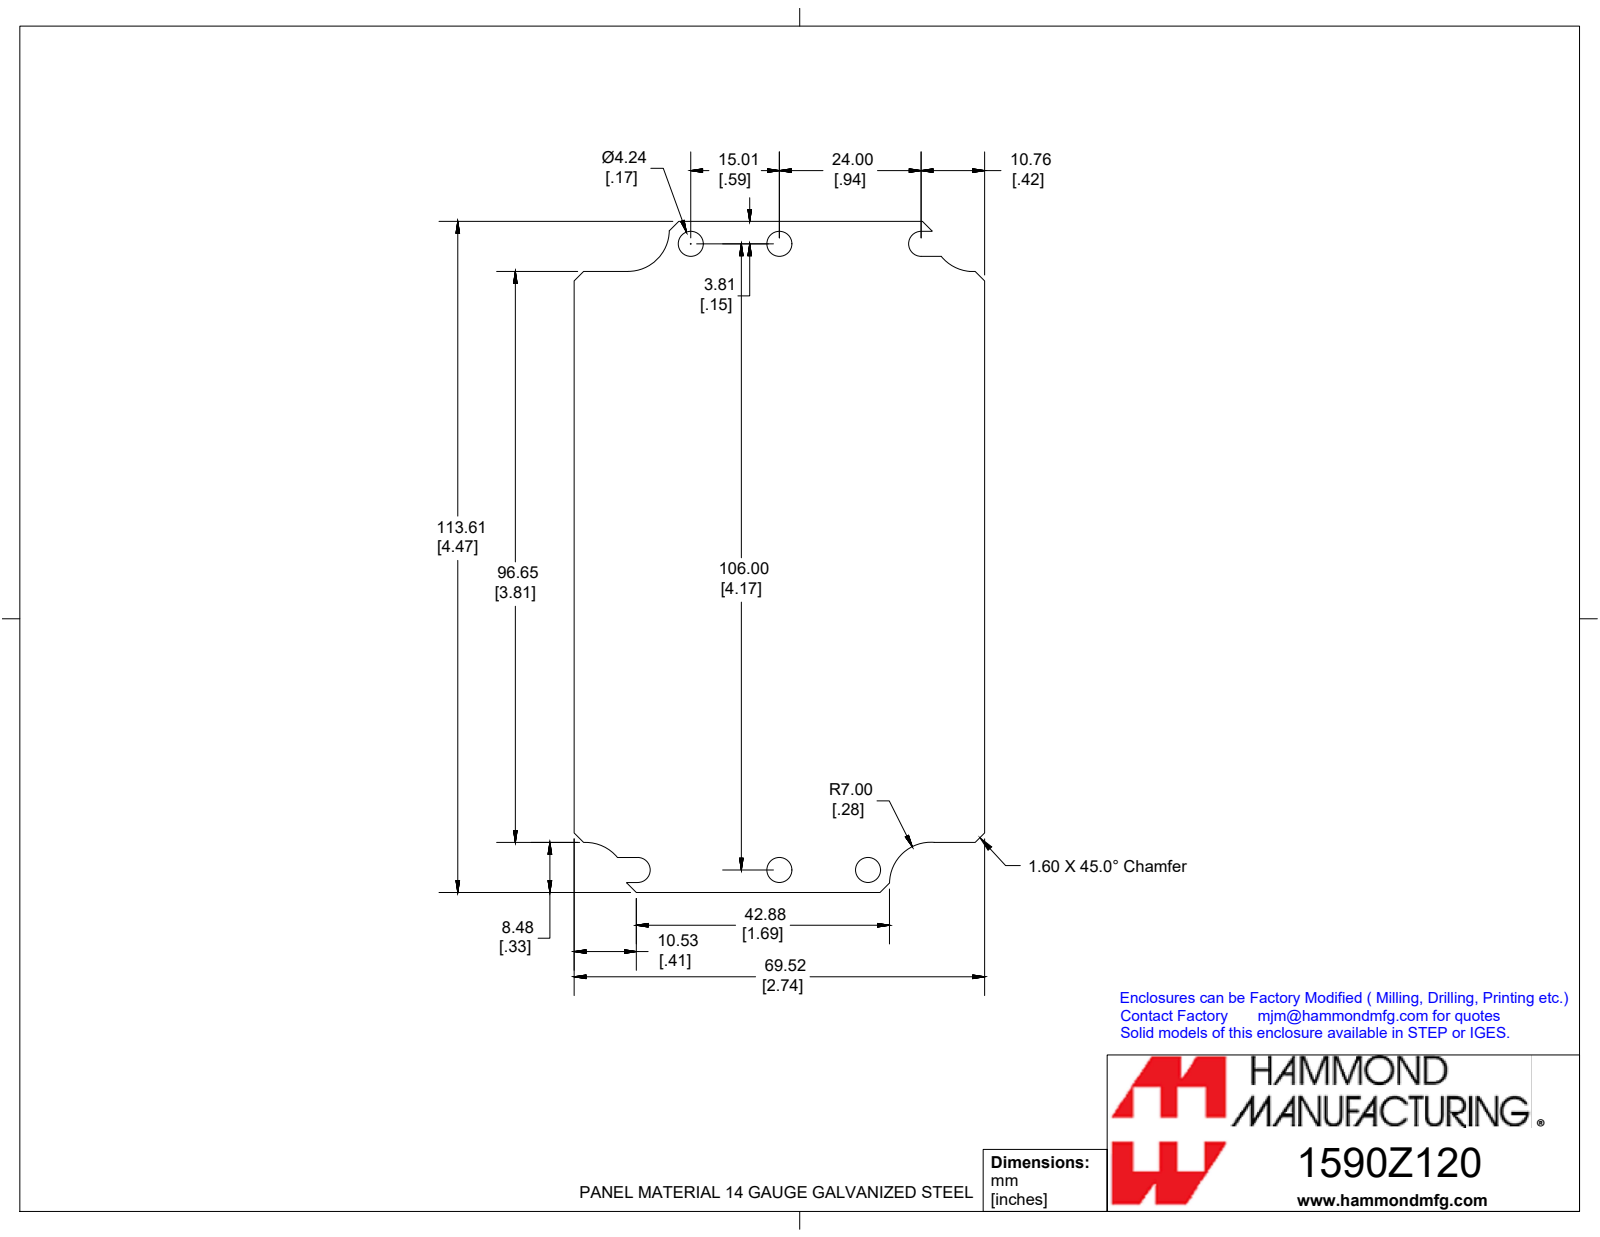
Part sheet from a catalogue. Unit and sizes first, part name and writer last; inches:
Units: inches
Overall size (bounding box): 4.473 × 2.737 × 0.064
Round holes (diameter × count): ⌀0.167 ×4
Partial cylindrical surfaces — rounded edges, fillets, slot ends (radius × count): R0.276 ×4, R0.084 ×2
Main face-to-face distances: 0.064, 2.737, 4.473, 0.334, 4.139, 3.805, 0.233, 4.24, 0.101, 3.906
Hole centre spacings: 0.591, 4.215, 4.173, 4.337
Volume: 0.73 in³ · Surface area: 24.02 in²
Bodies: 1 solid, 34 faces (22 planar, 12 cylindrical, 0 other)
Part name (STEP PRODUCT): 1590Z120PL
STEP written by: SolidWorks 2019 (CONFIG_CONTROL_DESIGN)
